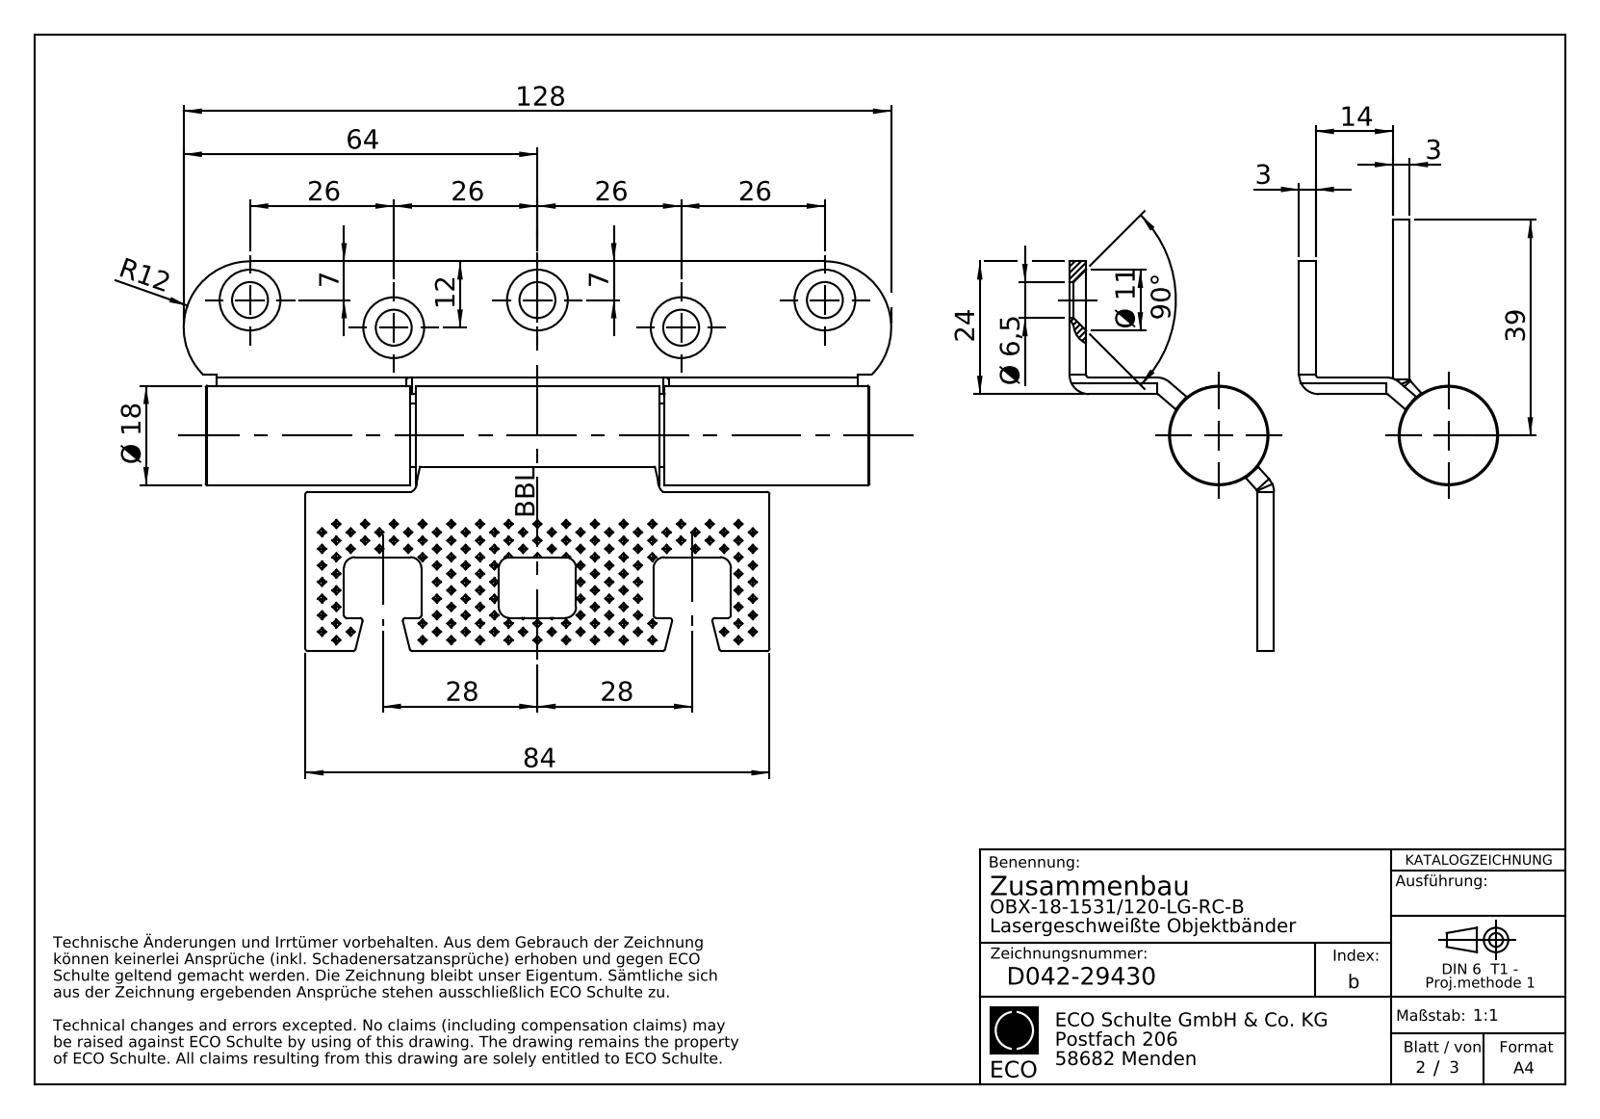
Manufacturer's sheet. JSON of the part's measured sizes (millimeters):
{"part_name": "D044-24252; D046-14312; DIN5401-III; B01572 (+4 more)", "step_written_by": "SolidWorks 2020 (CONFIG_CONTROL_DESIGN)", "units": "millimeters", "bodies": {"solids": 11, "faces": 1730, "planar": 1490, "cylindrical": 137, "other": 103}, "overall_size": [128, 48, 36], "volume_mm3": 49035, "surface_area_mm2": 29917, "round_holes": [[6.5, 5], [2, 2], [0.5, 1], [4.5, 1], [7.9, 1]], "round_bosses_or_shafts": [[18, 1], [12, 1], [11.8, 1], [11.5, 1], [7.7, 1], [4, 1], [1.65, 1]], "partial_cylinders_radius": [[0.5, 19], [2, 8], [0.25, 6], [3.5, 3], [0.68, 2], [2.1, 2], [3, 2], [12, 2]], "face_to_face_distances": [3, 17, 20, 14, 11.5, 82, 108.5, 25.5, 21, 24], "hole_center_spacings": [26.48, 52, 78.16, 1.95, 4.25, 4.6, 104]}
